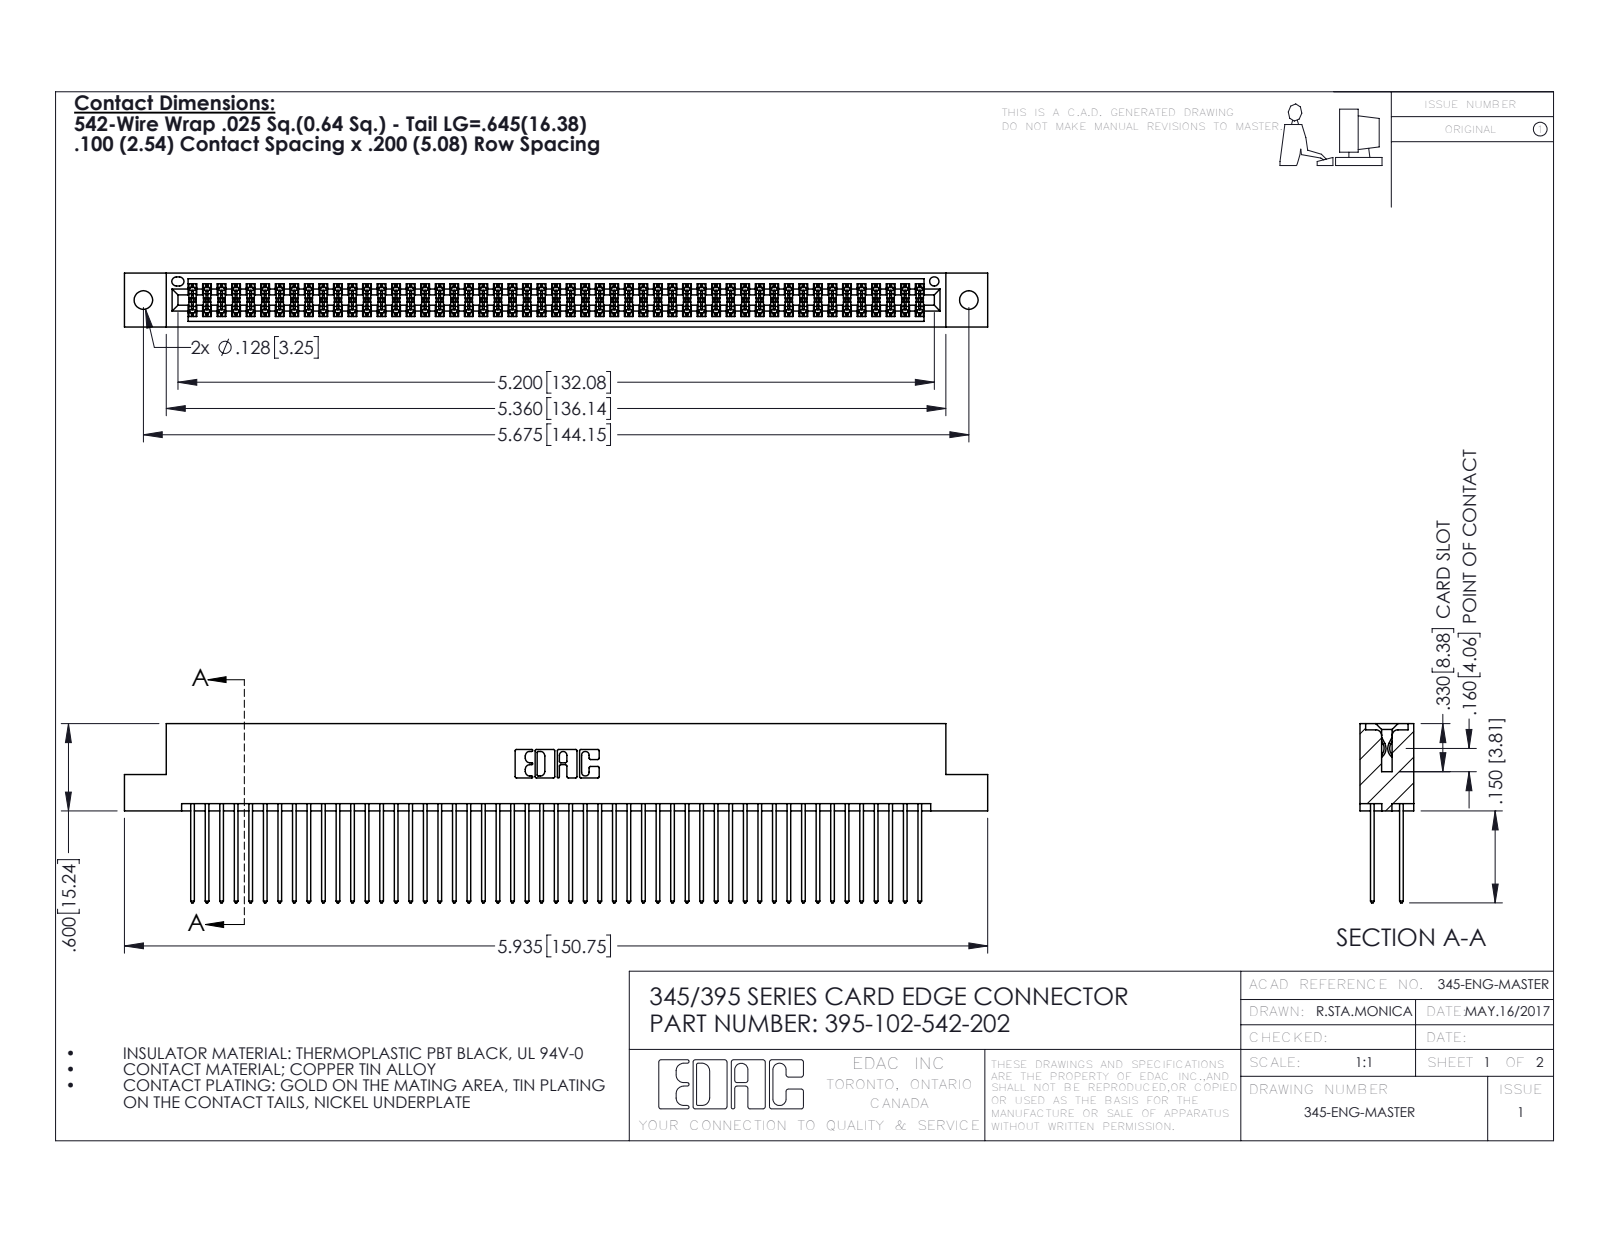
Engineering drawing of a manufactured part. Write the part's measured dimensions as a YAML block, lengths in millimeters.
part_name: "345 Part_Flush Mounting Lugs - 0.128 Dia; 395-102-542-202; 345-292-001_345-293-142"
step_written_by: "SolidWorks 2016 (CONFIG_CONTROL_DESIGN)"
units: millimeters
bodies: {solids: 103, faces: 5226, planar: 3446, cylindrical: 1780, other: 0}
overall_size: [150.7, 31.3, 9.4]
volume: 15200
surface_area: 24540
round_holes:
  - {diameter: 3.3, count: 2}
  - {diameter: 1.6, count: 1}
partial_cylinders:
  - {radius: 0.2, count: 153}
  - {radius: 0.3, count: 102}
  - {radius: 0.3, count: 22}
  - {radius: 0.2, count: 6}
  - {radius: 0.8, count: 6}
  - {radius: 0.7, count: 3}
  - {radius: 0.4, count: 2}
  - {radius: 0.5, count: 2}
face_to_face_distances: [7.6, 1.8, 5.1, 2.5, 6.9, 0.6, 5.7, 9.4, 4.4, 3.8]
hole_center_spacings: [6.9, 138.2, 144.1]
